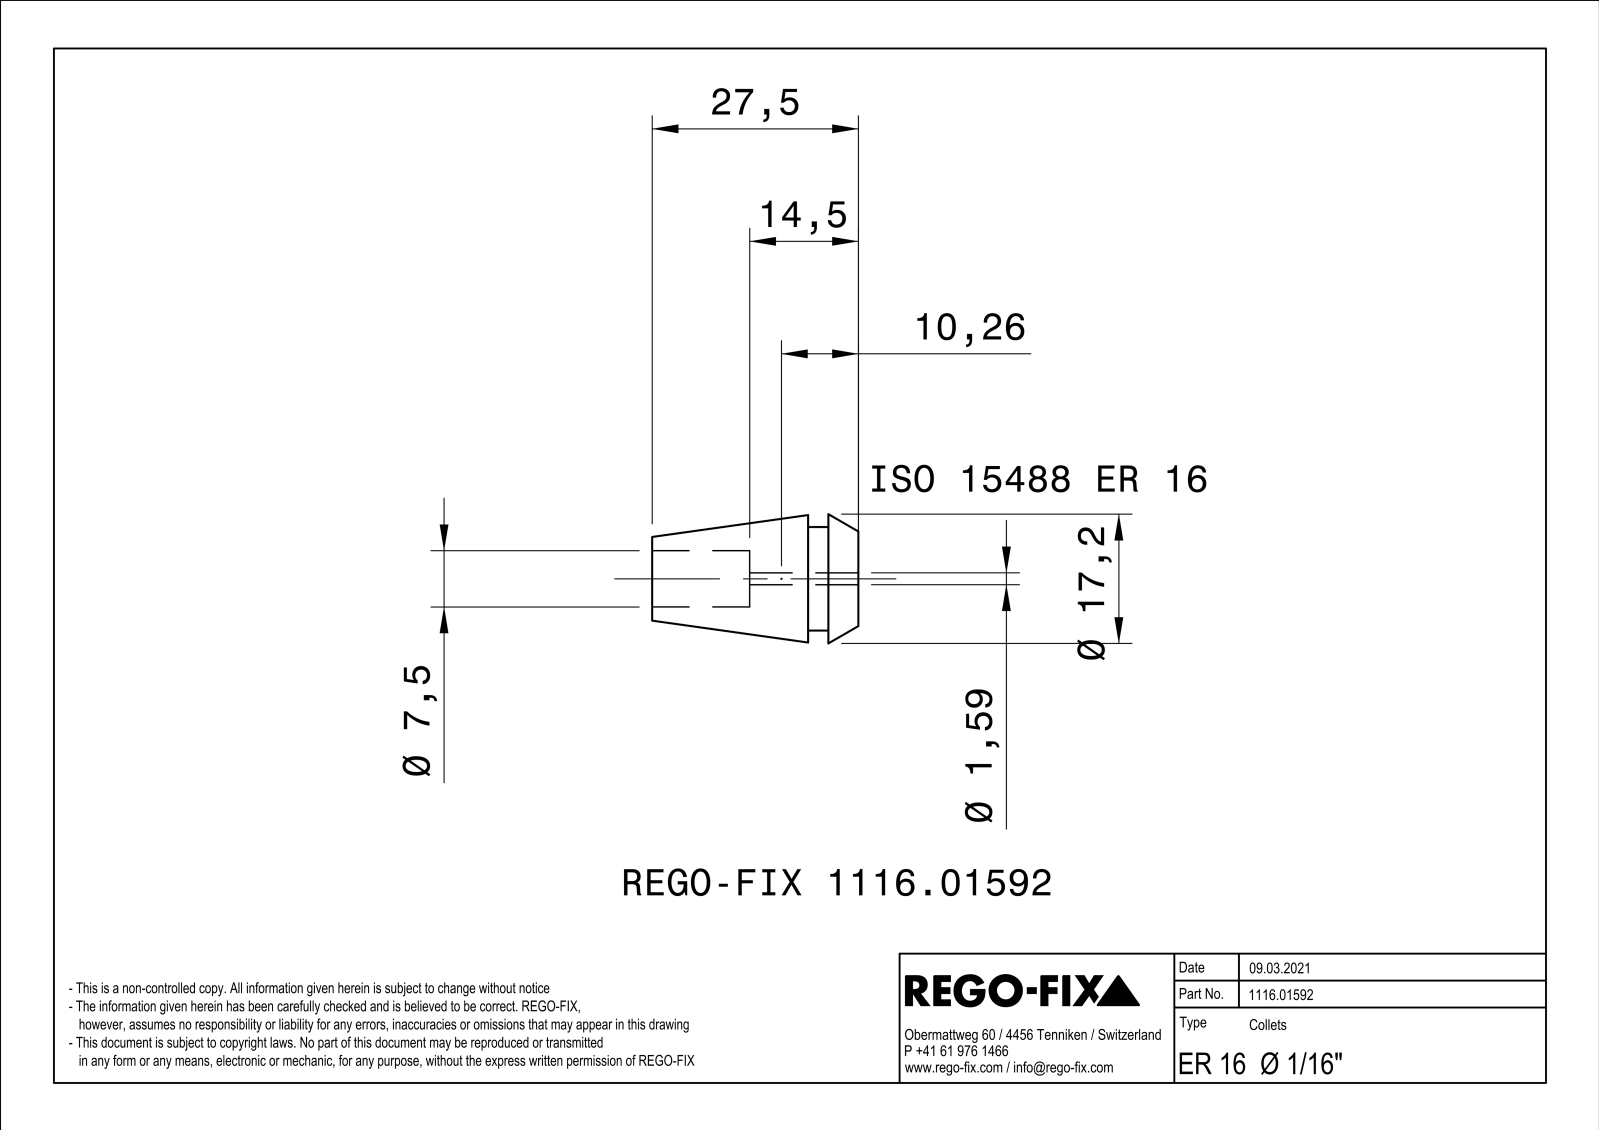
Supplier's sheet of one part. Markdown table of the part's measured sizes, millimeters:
| quantity | value |
| --- | --- |
| part name | NOCUT |
| STEP written by | SIEMENS PLM Software Solid Edge ST10 (AUTOMOTIVE_DESIGN) |
| units | millimeters |
| bodies | 1 solid, 224 faces (108 planar, 28 cylindrical, 88 other) |
| overall size | 27.5 × 17.24 × 17.24 |
| volume | 3 039 mm³ |
| surface area | 5 080 mm² |
| round holes (diameter × count) | 7.5 × 1 |
| round bosses / shafts (diameter × count) | 13.8 × 1 |
| partial cylindrical surfaces (radius × count) | 0.79 × 1 |
| main face-to-face distances | 0.46, 0.44, 0.45, 4, 6.7, 2.7, 3.27, 3.28, 3.72, 3.73 |
